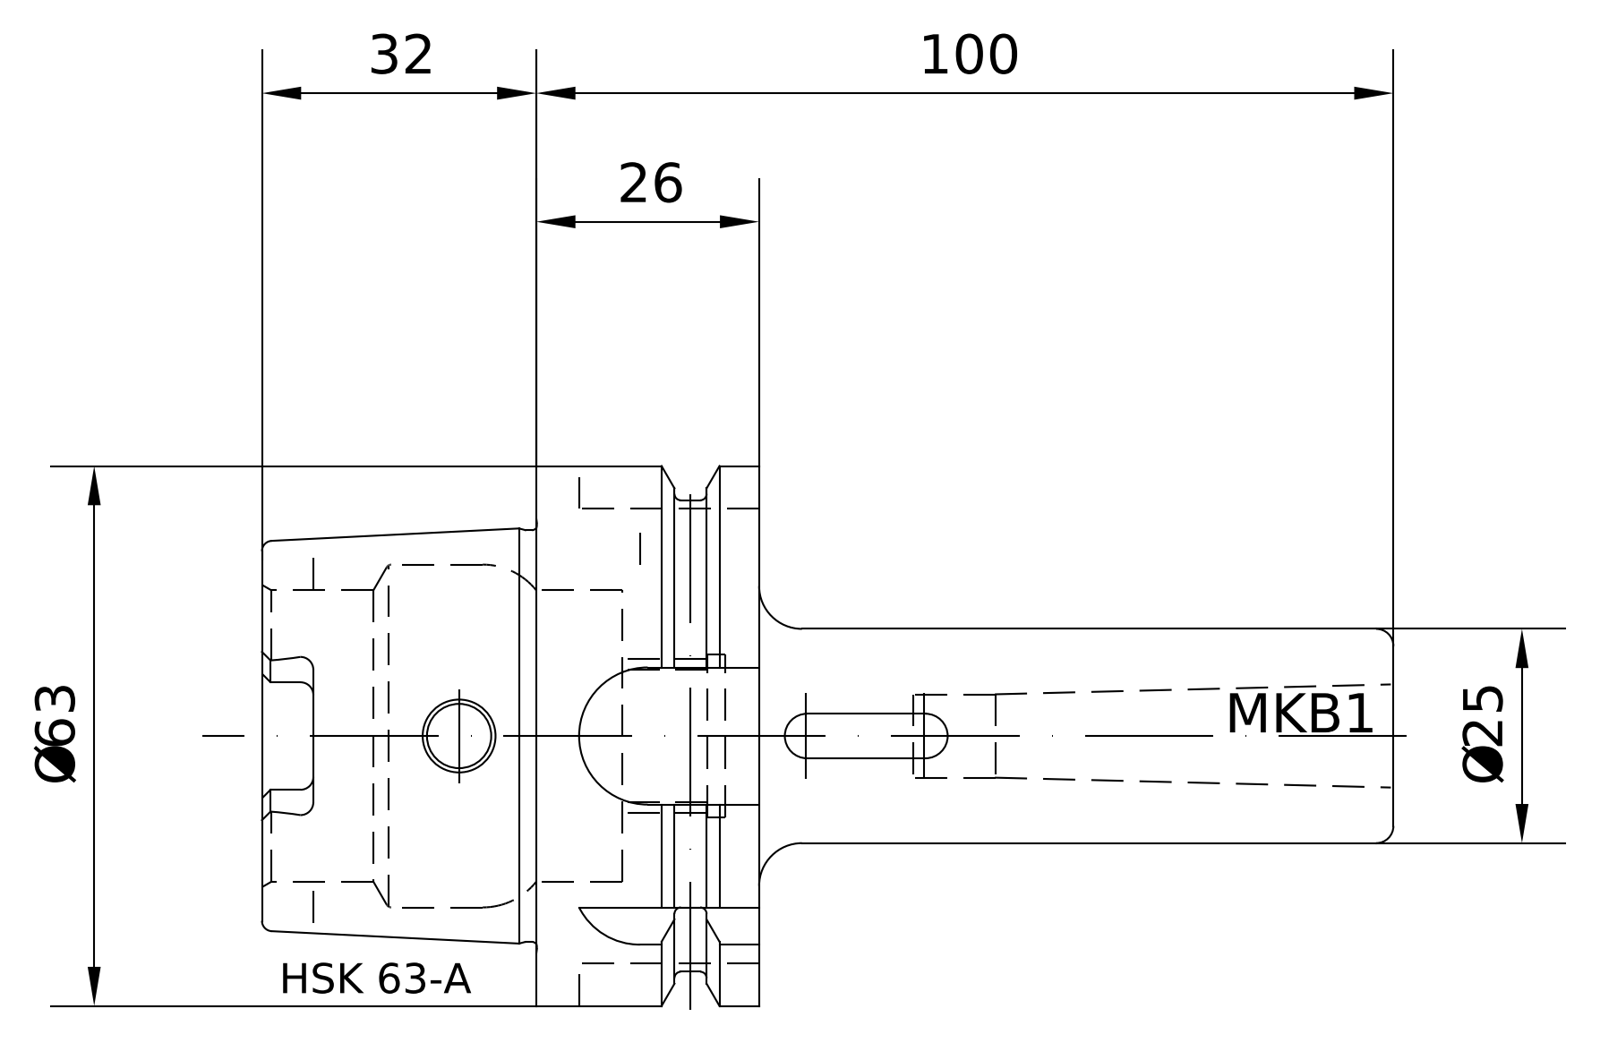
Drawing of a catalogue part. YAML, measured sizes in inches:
part_name: "A63-080-01"
step_written_by: "PRO/ENGINEER BY PARAMETRIC TECHNOLOGY CORPORATION, 2010430 (CONFIG_CONTROL_DESIGN)"
units: inches
bodies: {solids: 1, faces: 173, planar: 57, cylindrical: 48, other: 68}
overall_size: [5.197, 2.48, 2.48]
volume: 6.918
surface_area: 46.5
round_holes:
  - {diameter: 0.295, count: 1}
  - {diameter: 0.382, count: 1}
  - {diameter: 0.394, count: 1}
  - {diameter: 0.666, count: 1}
  - {diameter: 0.721, count: 1}
  - {diameter: 0.735, count: 1}
  - {diameter: 1.339, count: 1}
  - {diameter: 1.575, count: 1}
round_bosses_or_shafts:
  - {diameter: 2.48, count: 1}
  - {diameter: 2.165, count: 1}
  - {diameter: 1.891, count: 1}
  - {diameter: 0.984, count: 1}
  - {diameter: 0.709, count: 1}
partial_cylinders:
  - {radius: 0.059, count: 6}
  - {radius: 0.118, count: 4}
  - {radius: 0.315, count: 1}
  - {radius: 0.316, count: 1}
  - {radius: 0.355, count: 1}
face_to_face_distances: [1.024, 0.394, 0.63, 1.26, 1.654, 2.283, 2.079, 2.118, 0.858, 0.465]
